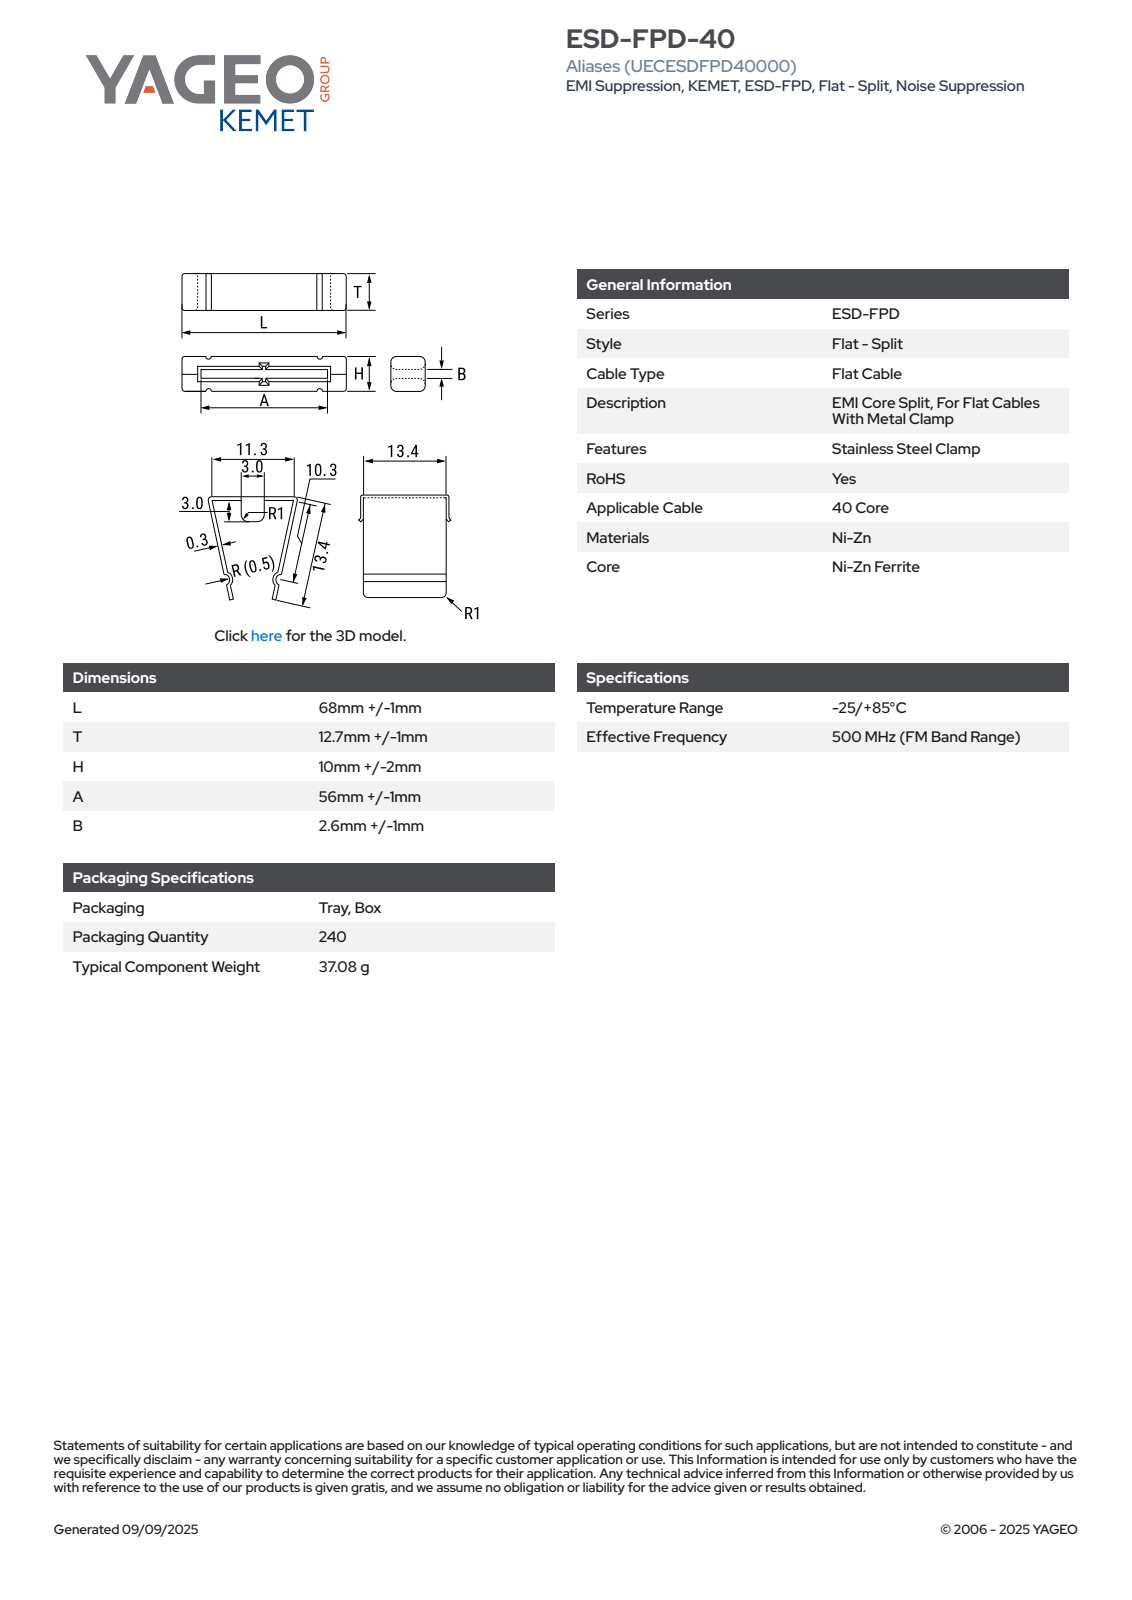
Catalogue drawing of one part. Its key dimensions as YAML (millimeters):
part_name: "EC_FPD_L69T13.7H12A56B2.6"
step_written_by: "SolidWorks 2021 (AUTOMOTIVE_DESIGN)"
units: millimeters
bodies: {solids: 4, faces: 91, planar: 79, cylindrical: 12, other: 0}
overall_size: [69, 12.7, 12]
volume: 8603
surface_area: 4828
partial_cylinders:
  - {radius: 0.5, count: 8}
  - {radius: 0.62, count: 4}
face_to_face_distances: [4.7, 7.3, 12, 2.6, 12.7, 69, 16.76, 6.5, 62.5, 56]
